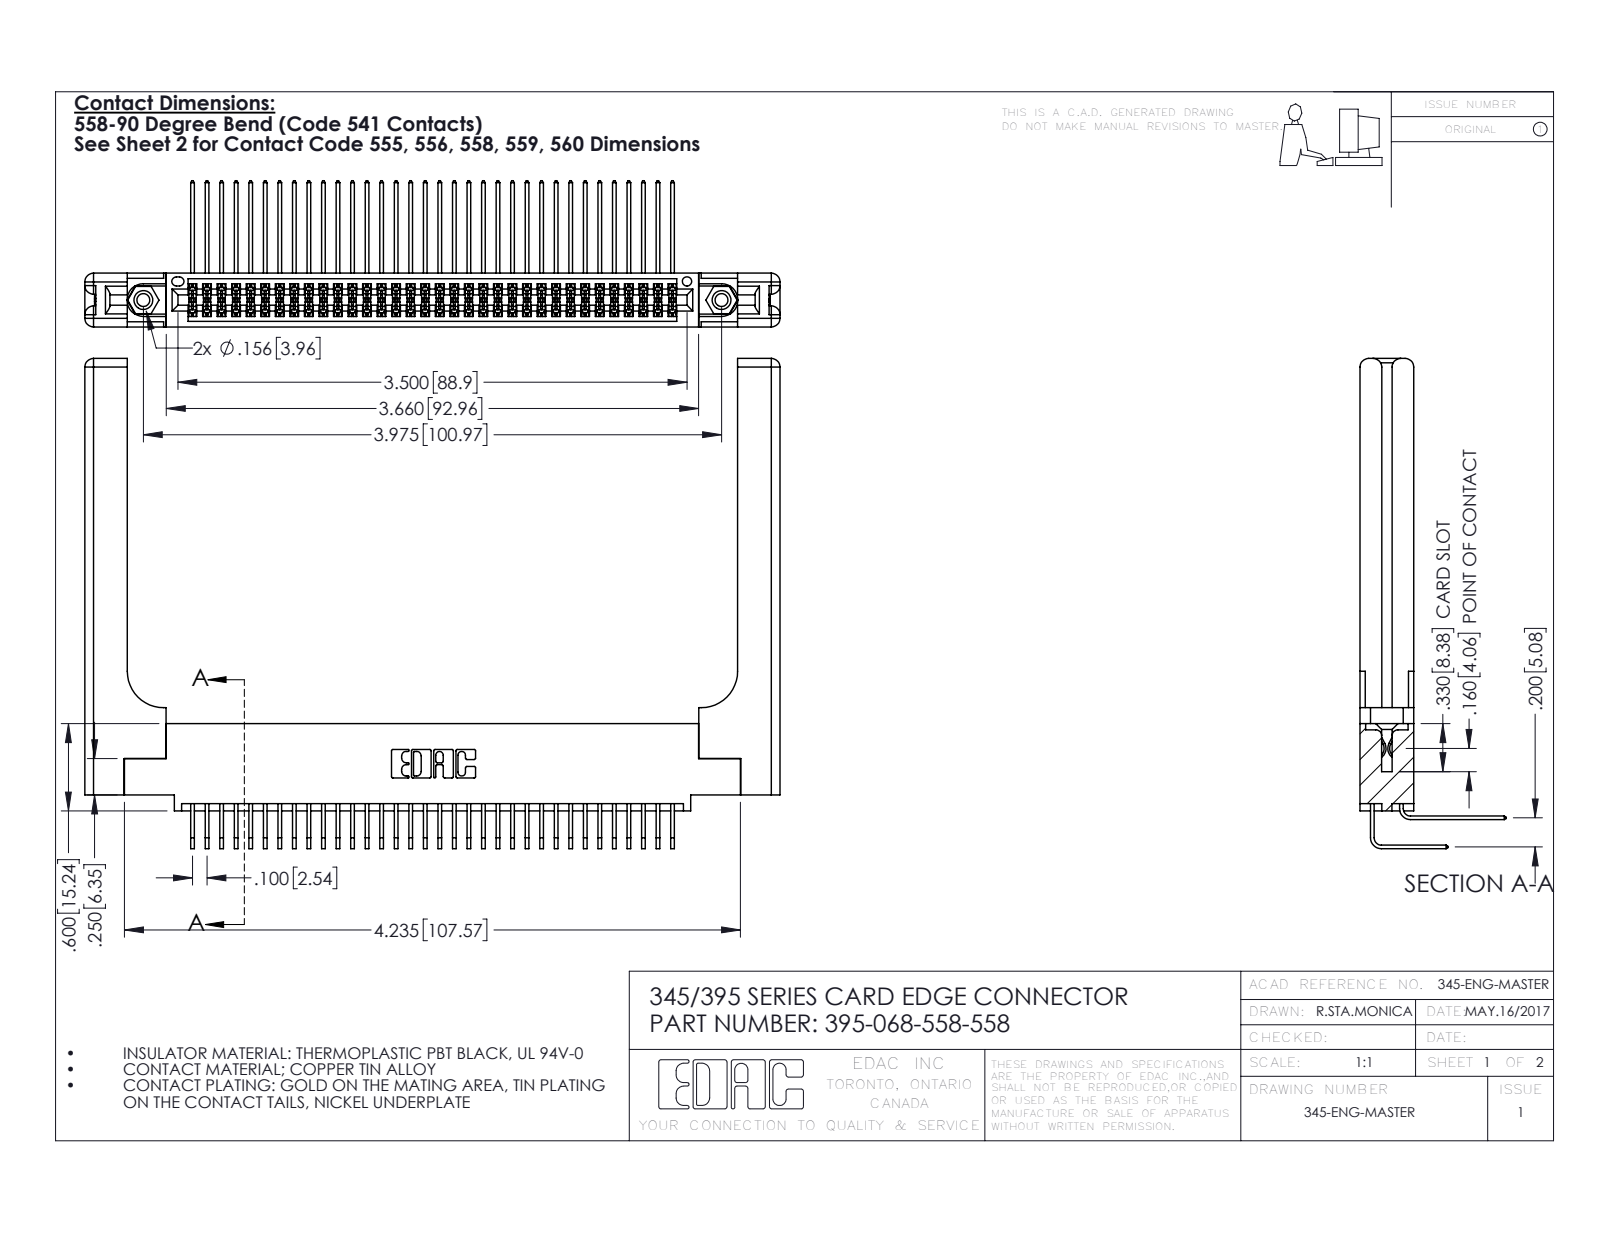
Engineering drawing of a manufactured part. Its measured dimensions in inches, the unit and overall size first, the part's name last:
Units: inches
Overall size (bounding box): 4.779 × 3.369 × 1.005
Round holes (diameter × count): ⌀0.089 ×2, ⌀0.125 ×2, ⌀0.156 ×2, ⌀0.064 ×1
Round bosses / shafts (diameter × count): ⌀0.155 ×2
Partial cylindrical surfaces — rounded edges, fillets, slot ends (radius × count): R0.006 ×103, R0.01 ×22, R0.06 ×16, R0.007 ×6, R0.031 ×6, R0.026 ×3, R0.014 ×2, R0.019 ×2
Main face-to-face distances: 0.072, 0.37, 0.298, 0.2, 0.098, 0.272, 0.025, 0.225, 0.148, 0.15
Hole centre spacings: 0.27, 3.74, 3.975
Volume: 1.252 in³ · Surface area: 38.18 in²
Bodies: 73 solids, 3922 faces (2612 planar, 1250 cylindrical, 60 other)
Part name (STEP PRODUCT): 345-250-001_345-250-001-102; 395-068-558-558; 345-220-058_345-220-058; 345-292-001_558 Tail - 2 (+2 more)
STEP written by: SolidWorks 2016 (CONFIG_CONTROL_DESIGN)
